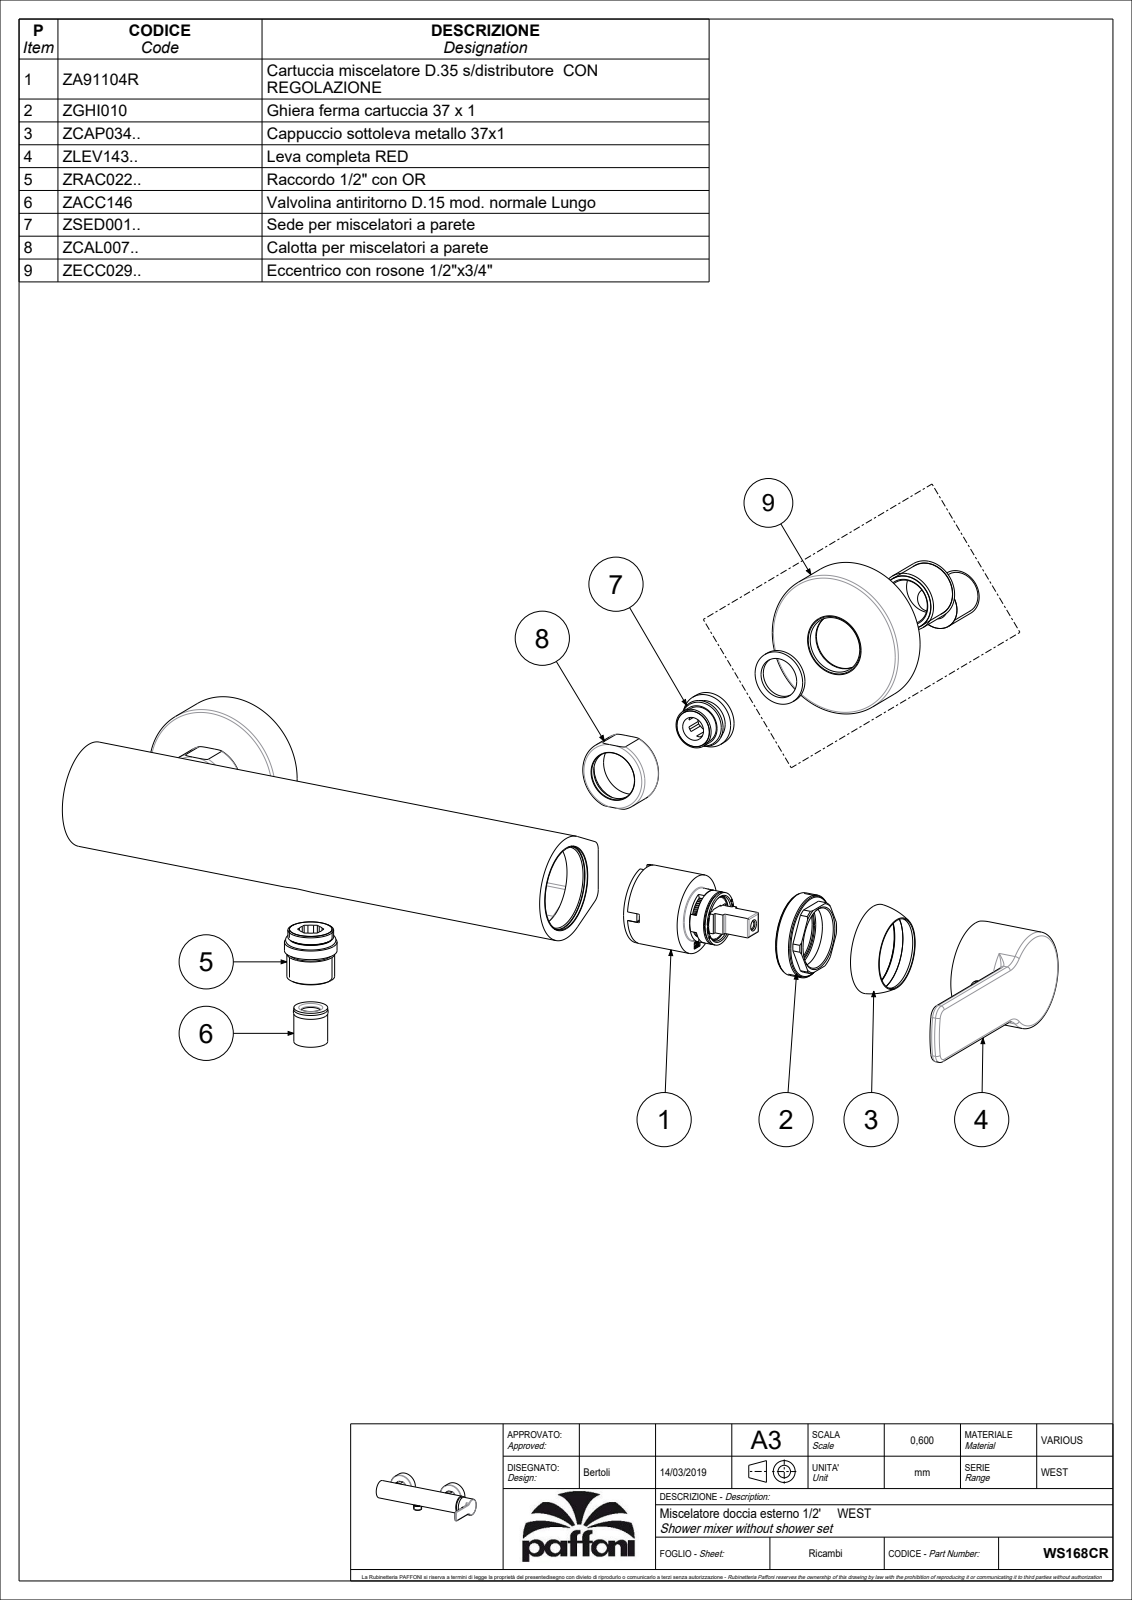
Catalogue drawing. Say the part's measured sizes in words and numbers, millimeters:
The part is named "WS168CR_SW0001". Its 3-D file was written by "CREO PARAMETRIC BY PTC INC, 2019030 (CONFIG_CONTROL_DESIGN)". It is 1 solid with 265 faces: 68 planar, 92 cylindrical and 105 other. Overall it measures 277.6 by 167.5 by 67.2 millimeters. Its volume is 663 065 cubic millimeters and its surface area 83 198 square millimeters. Round holes: 1 of diameter 3, 1 of diameter 23.8. Round bosses or shafts: 2 of diameter 64.5, 2 of diameter 20.5, 1 of diameter 43, 1 of diameter 23, 1 of diameter 20.9, 1 of diameter 7.6, 1 of diameter 5.5. Partial cylindrical surfaces (rounded edges, fillets, slot ends): 39 of radius 0.5, 4 of radius 1.5, 4 of radius 5, 2 of radius 10, 2 of radius 15.6, 2 of radius 18.5, 1 of radius 23.25, 1 of radius 50. The main face-to-face distances are 20, 15, 35, 277.6, 273.1, 4.5, 15.5, 35.5, 0.5, 33.7.
